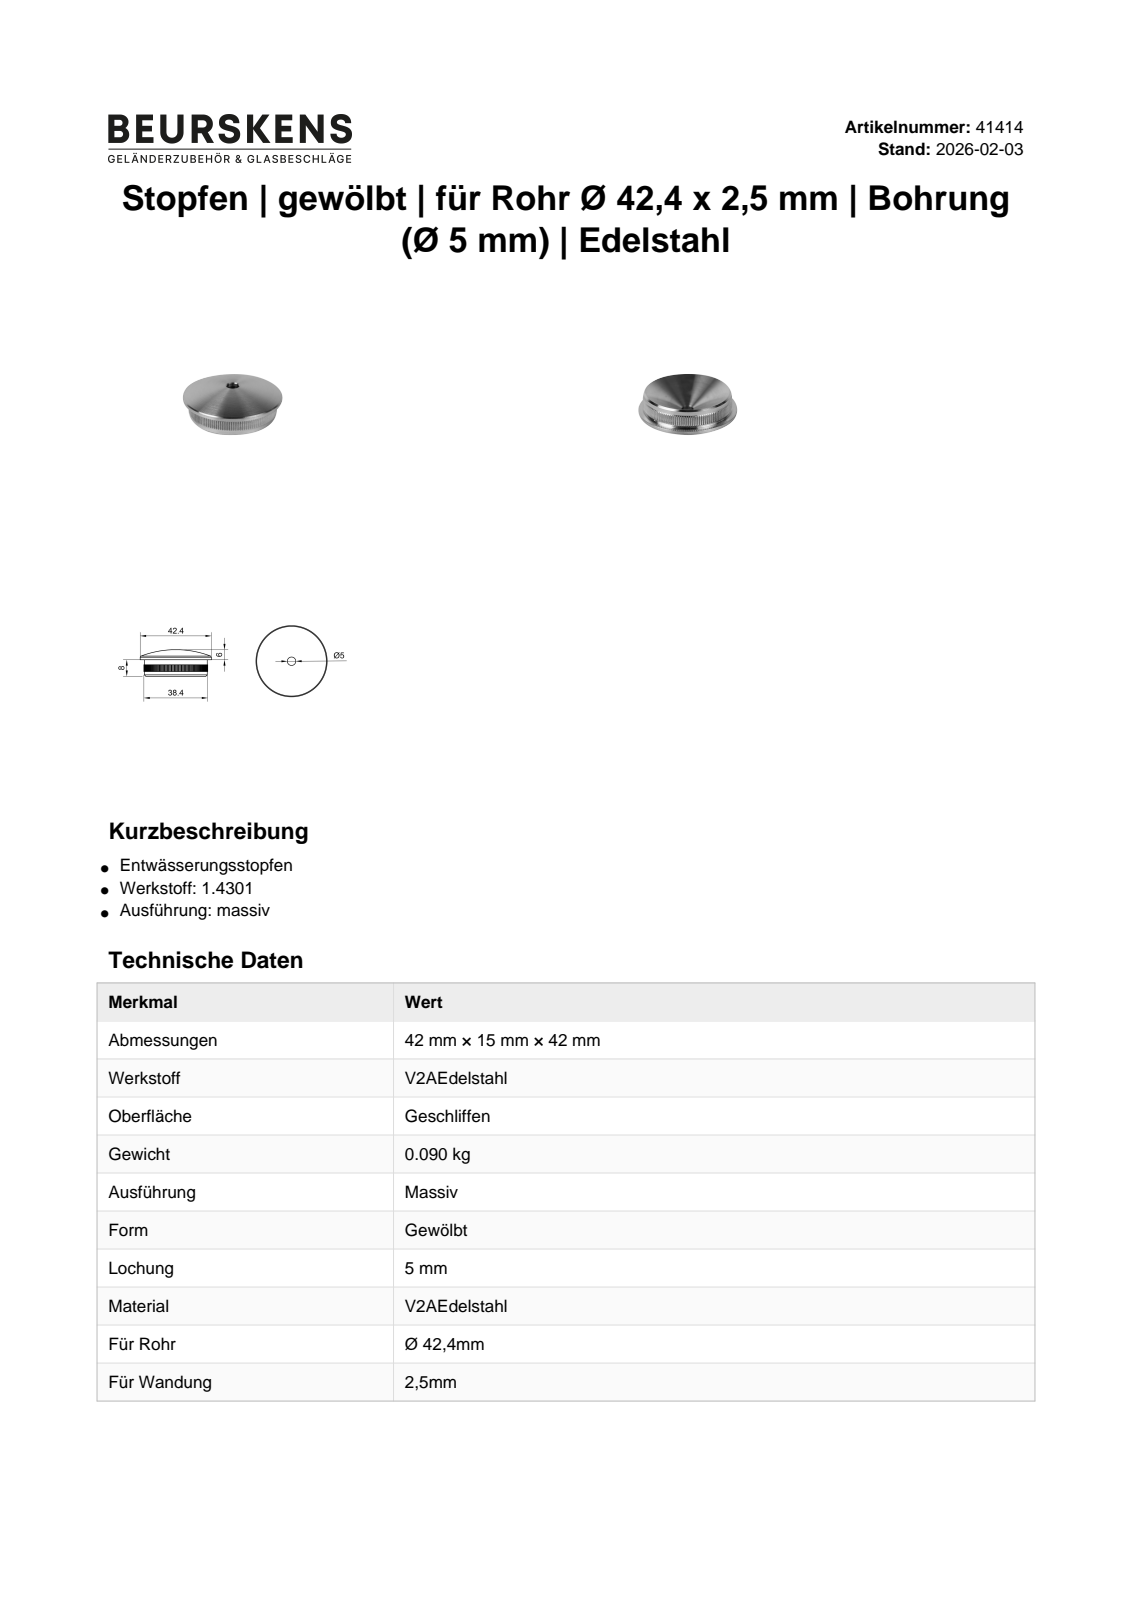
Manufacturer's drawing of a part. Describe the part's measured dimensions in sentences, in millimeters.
The part is named "41414". Its 3-D file was written by "Autodesk Inventor 2022 (AUTOMOTIVE_DESIGN)". It is 1 solid with 291 faces: 3 planar, 284 cylindrical and 4 other. Overall it measures 42.4 by 42.4 by 15.82 millimeters. Its volume is 13 042 cubic millimeters and its surface area 4 588 square millimeters. Round holes: 1 of diameter 5. Round bosses or shafts: 1 of diameter 42.4, 1 of diameter 37.4. Partial cylindrical surfaces (rounded edges, fillets, slot ends): 140 of radius 0.12, 1 of radius 19. The main face-to-face distances are 7, 4, 3.
